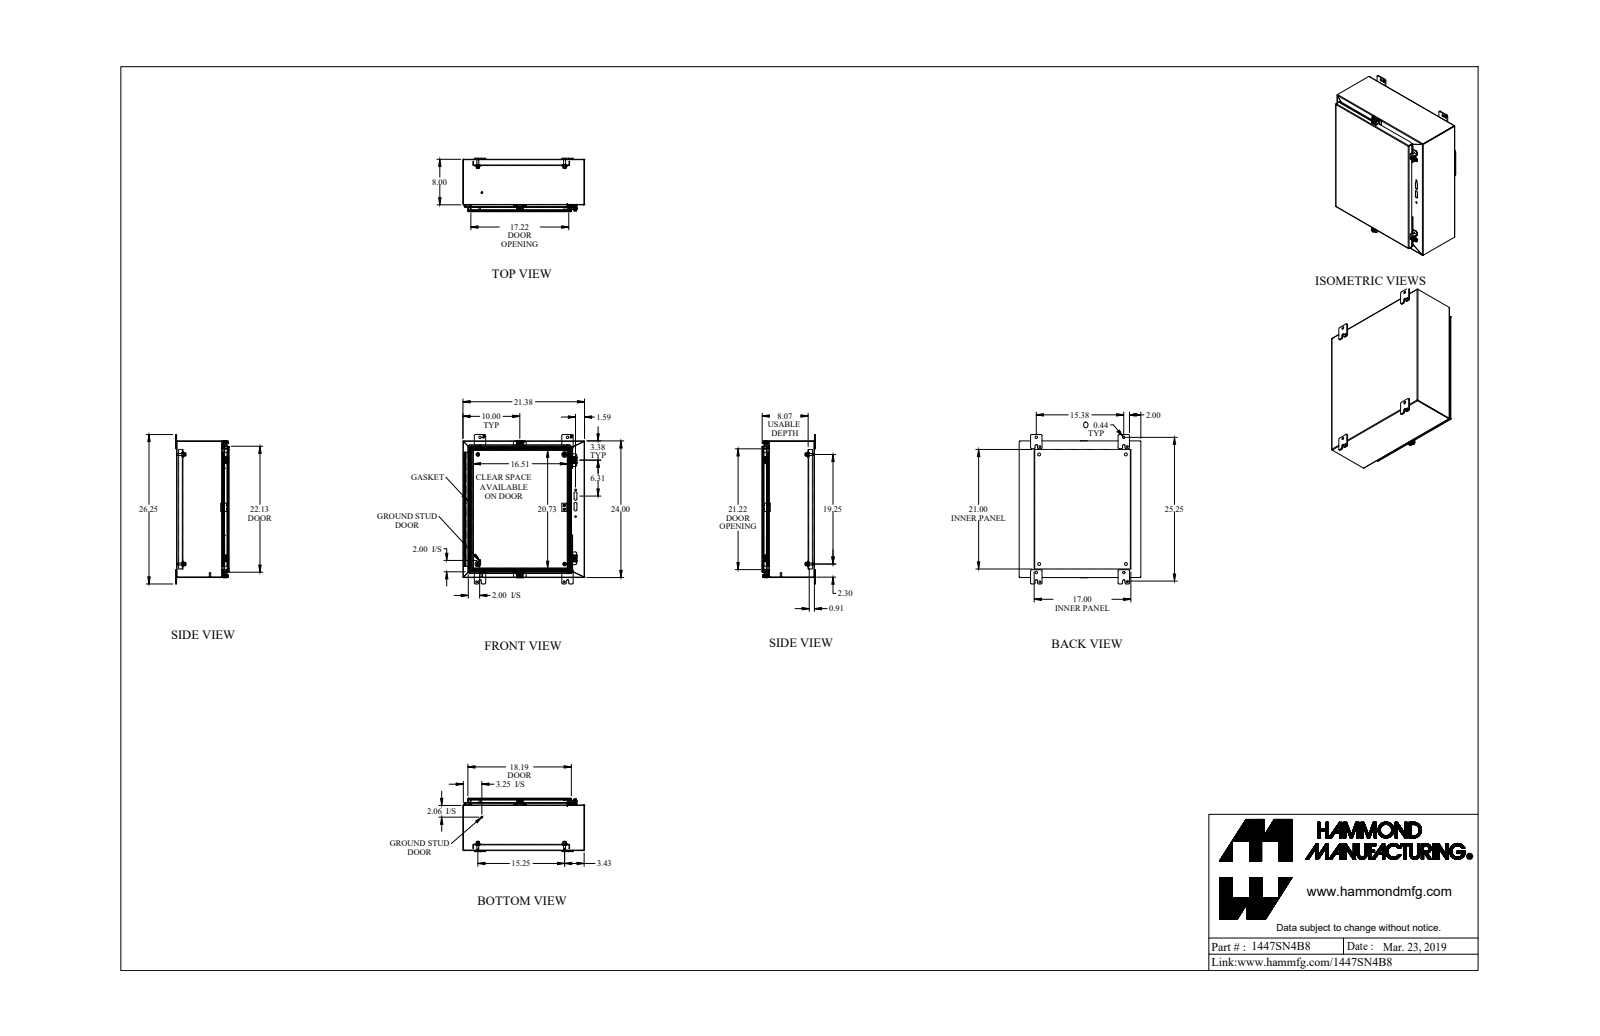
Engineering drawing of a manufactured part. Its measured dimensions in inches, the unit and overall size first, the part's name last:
Units: inches
Overall size (bounding box): 26.25 × 21.375 × 9.397
Round holes (diameter × count): ⌀0.313 ×6, ⌀0.213 ×4, ⌀0.375 ×4, ⌀0.437 ×4, ⌀0.5 ×4, ⌀0.15 ×2, ⌀0.156 ×2, ⌀0.265 ×2, ⌀0.265 ×2, ⌀0.281 ×2, ⌀0.307 ×2, ⌀0.187 ×1
Round bosses / shafts (diameter × count): ⌀0.65 ×4, ⌀0.5 ×4, ⌀0.39 ×4, ⌀0.375 ×4, ⌀0.33 ×4, ⌀0.25 ×4, ⌀0.244 ×4, ⌀1 ×2
Partial cylindrical surfaces — rounded edges, fillets, slot ends (radius × count): R0.188 ×24, R0.25 ×24, R0.036 ×23, R0.108 ×23, R0.048 ×21, R0.143 ×21, R0.045 ×10, R0.125 ×8
Main face-to-face distances: 0.072, 9.066, 9.138, 0.072, 9.138, 9.21, 21.303, 0.095, 8.106, 8.034
Hole centre spacings: 17.151, 2.122, 15.25, 15.375, 25.024, 1.735, 7.674, 10.235
Volume: 191.8 in³ · Surface area: 5 038 in²
Bodies: 42 solids, 1450 faces (860 planar, 497 cylindrical, 93 other)
Part name (STEP PRODUCT): 1447SN4B8_Default
STEP written by: SolidWorks 2019 (CONFIG_CONTROL_DESIGN)
